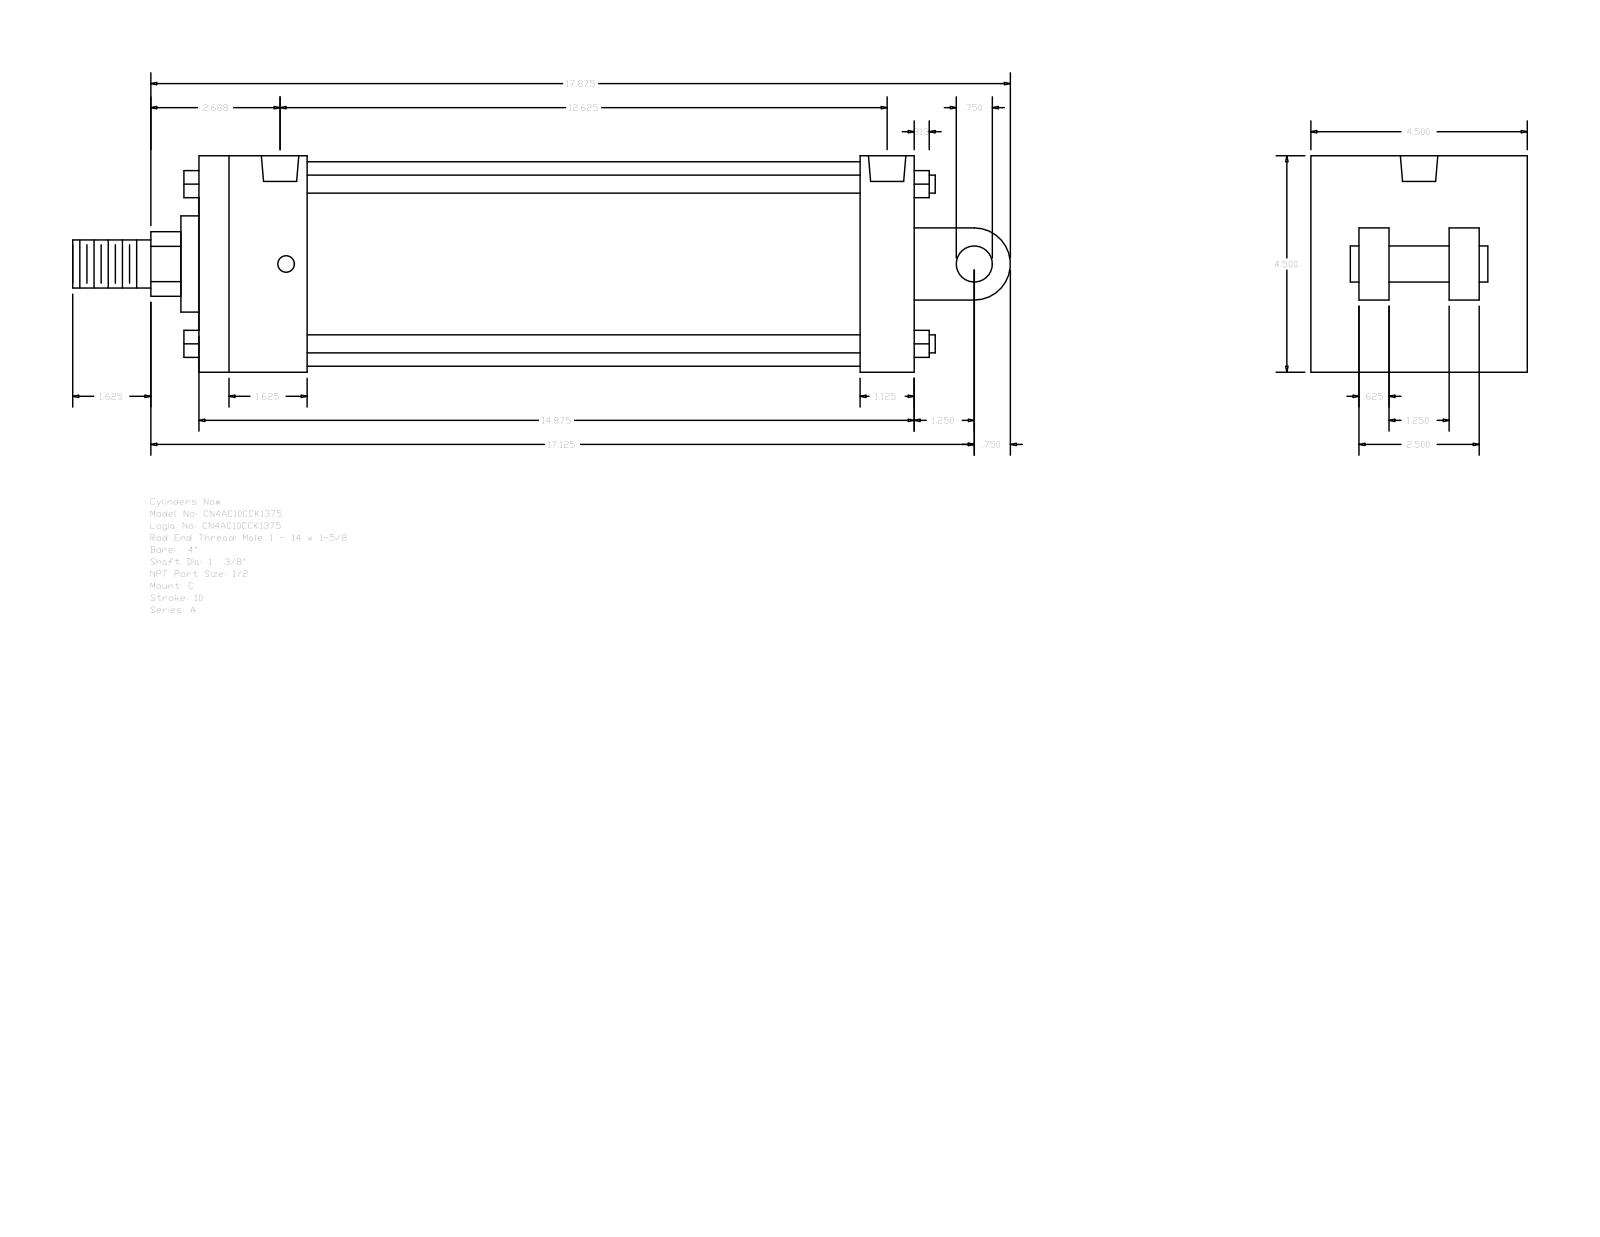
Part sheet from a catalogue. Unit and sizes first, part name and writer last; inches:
Units: inches
Overall size (bounding box): 19.5 × 4.5 × 4.5
Round holes (diameter × count): ⌀0.344 ×4, ⌀0.778 ×2
Round bosses / shafts (diameter × count): ⌀0.375 ×4, ⌀4.25 ×1, ⌀2 ×1, ⌀1.375 ×1, ⌀1 ×1, ⌀0.75 ×1
Partial cylindrical surfaces — rounded edges, fillets, slot ends (radius × count): R0.672 ×1, R0.75 ×1
Main face-to-face distances: 4.5, 14.875, 2.25, 1.125, 2.875, 13.75, 11.5, 12.625, 1.625, 1
Hole centre spacings: 0.125, 12.375, 12.5, 12.625
Bodies: 0 solids, 135 faces (102 planar, 33 cylindrical, 0 other)
Part name (STEP PRODUCT): A_C__0400_1.375
STEP written by: GSSL Pune (CONFIG_CONTROL_DESIGN)
